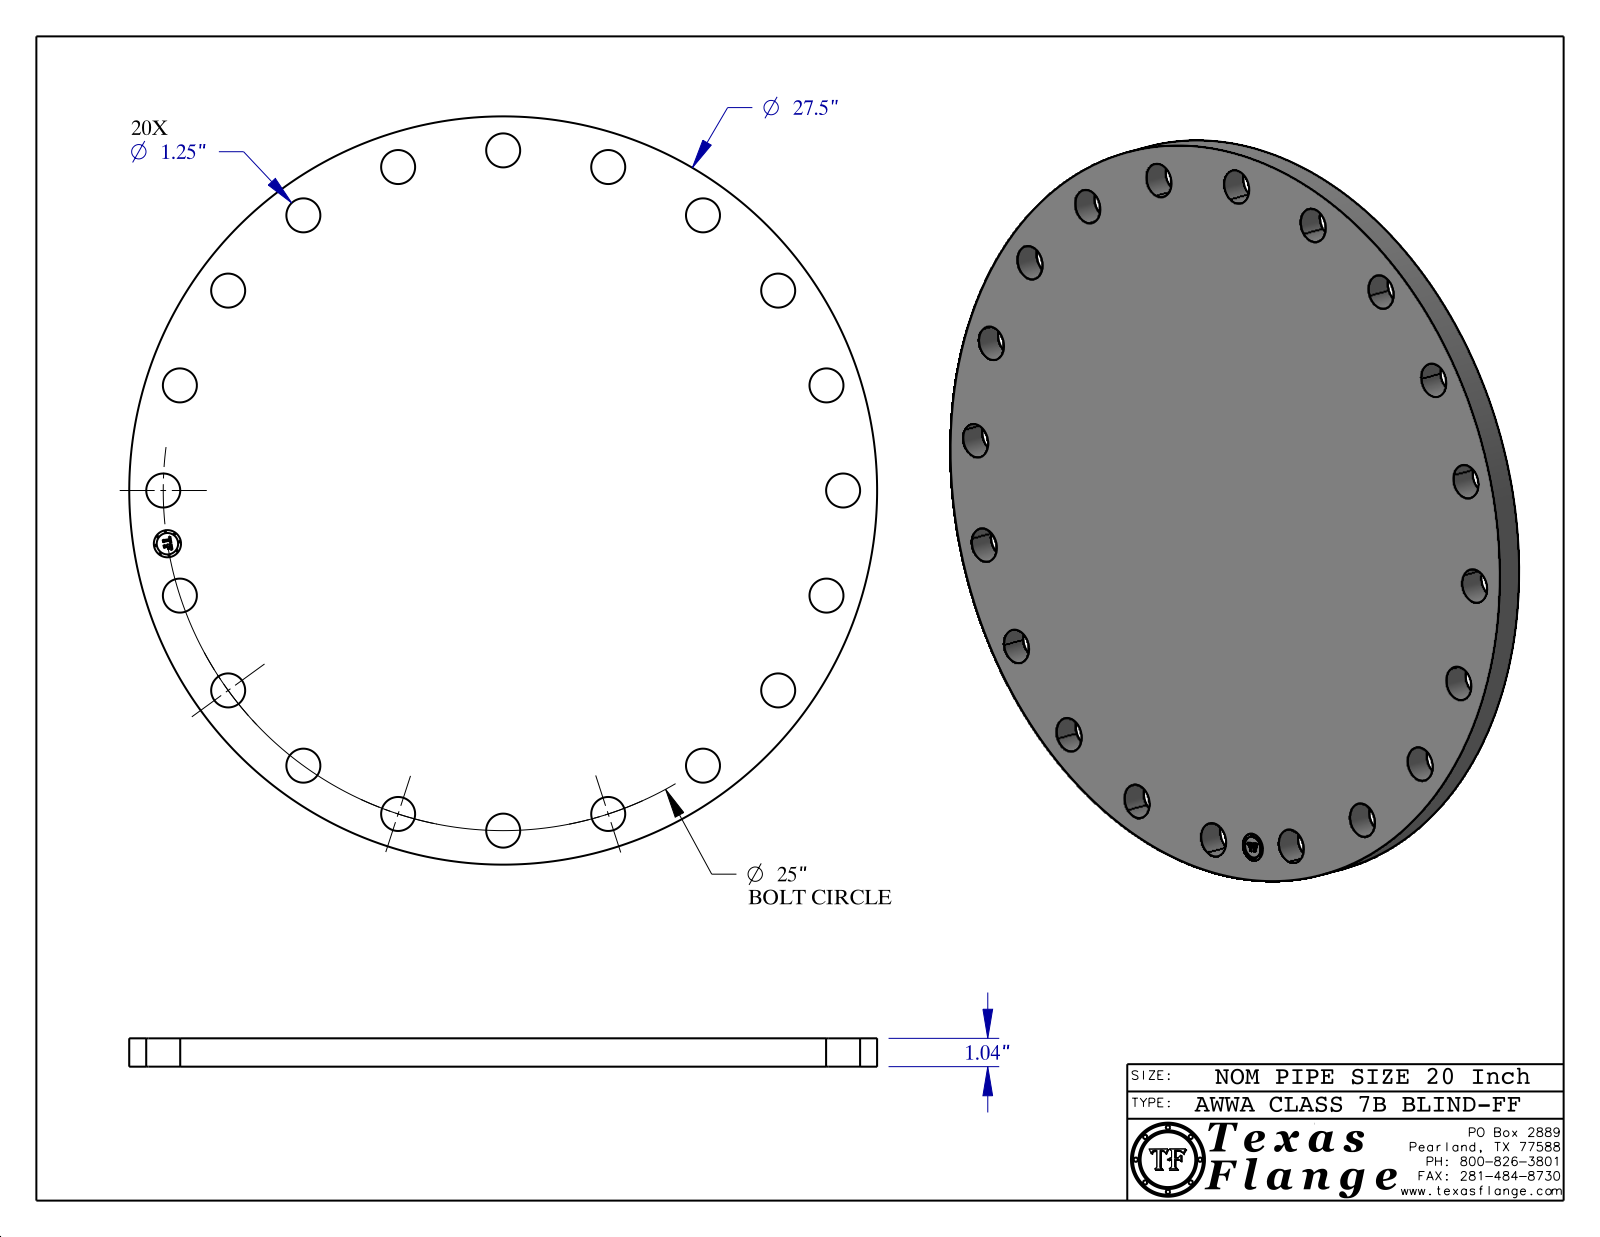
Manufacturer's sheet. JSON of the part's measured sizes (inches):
{"part_name": "AWWA Class 7B-BLIND-FF", "step_written_by": "CATIA V5 STEP AP214 (AUTOMOTIVE_DESIGN)", "units": "inches", "bodies": {"solids": 1, "faces": 429, "planar": 367, "cylindrical": 62, "other": 0}, "overall_size": [27.5, 27.5, 1.04], "volume_in3": 592.2, "surface_area_in2": 1311, "round_holes": [[1.25, 20], [1, 1]], "round_bosses_or_shafts": [[0.061, 8], [27.5, 1], [0.788, 1]], "face_to_face_distances": [1.04, 0.015, 1.025, 0.019, 0.298, 0.293, 0.054, 0.194, 0.248, 0.044], "hole_center_spacings": [14.694, 17.678, 20.225, 23.776, 24.692, 11.35, 22.275, 3.911]}
